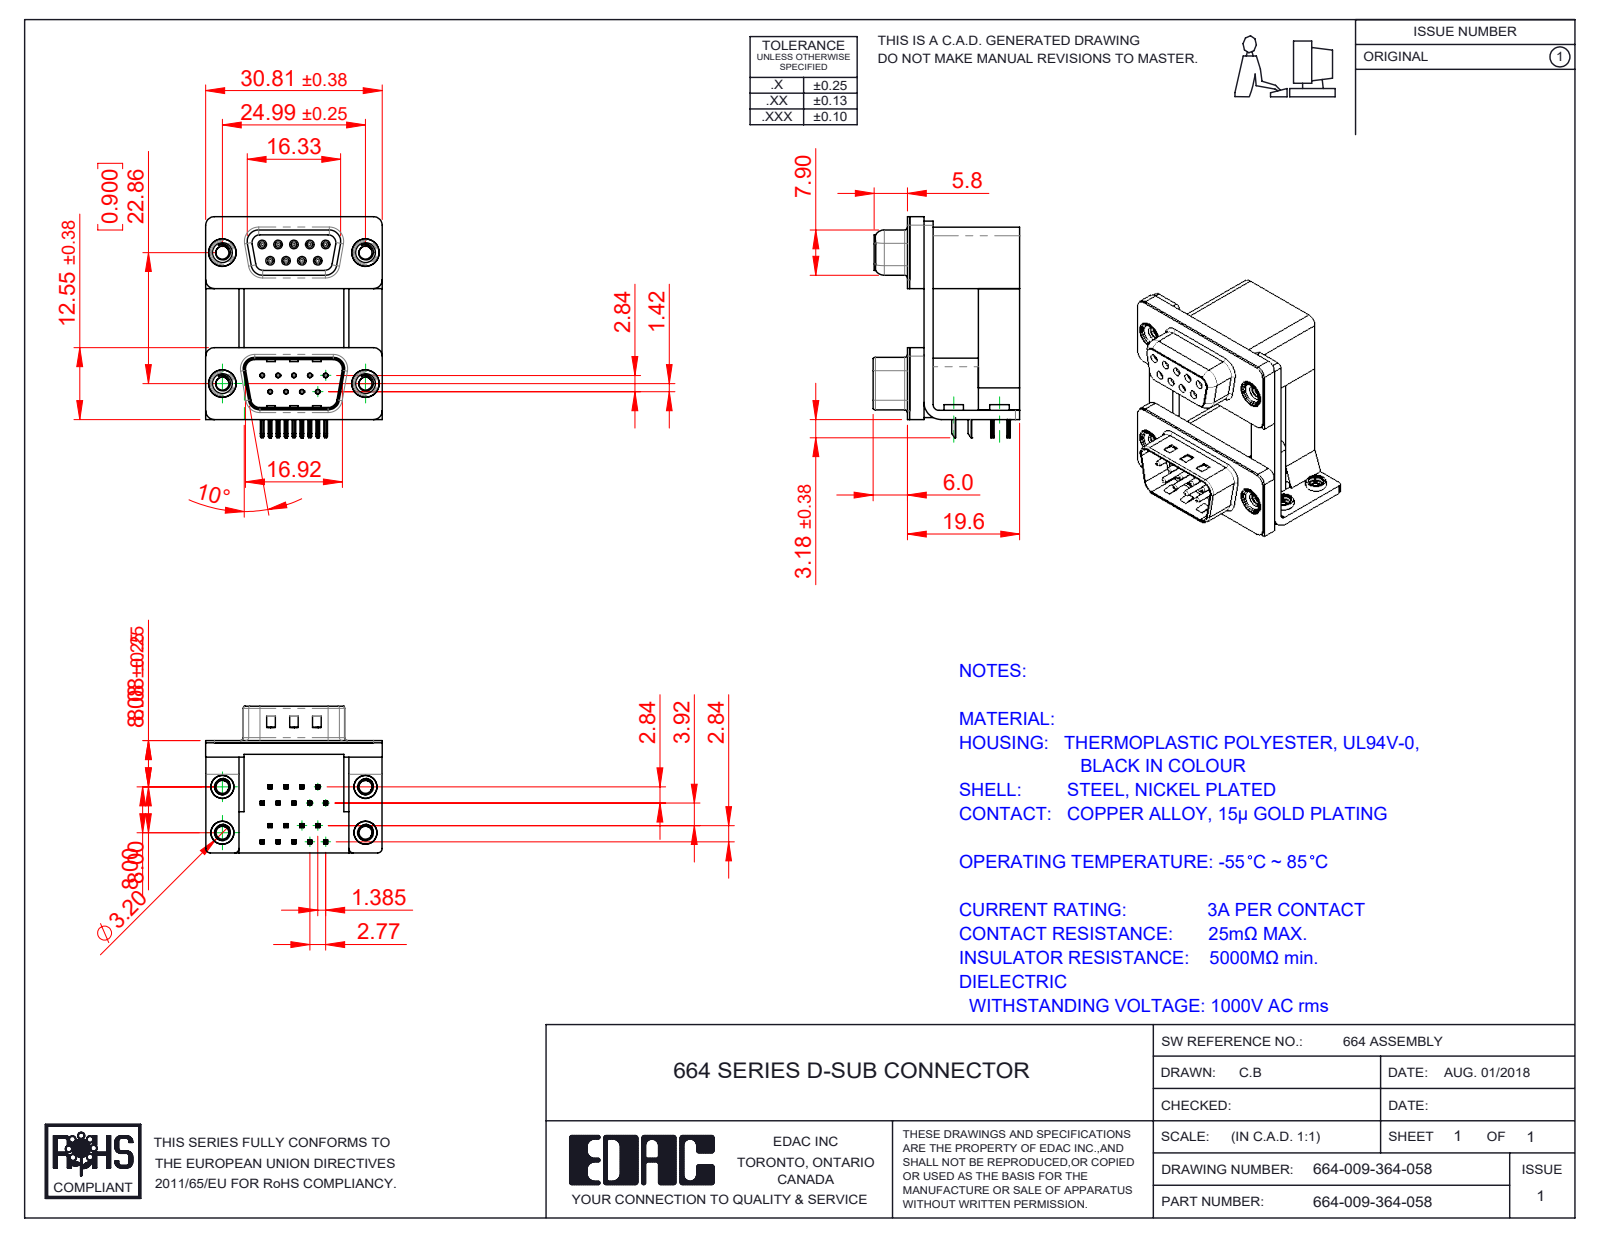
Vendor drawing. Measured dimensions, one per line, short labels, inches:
name: 664 Housing Upper_09 Contacts H; 664-009-364-058; 664 Contact Bottom Upper_H; 664 Threaded Rivet_4-40 (+8 more)
written by: SolidWorks 2020 (CONFIG_CONTROL_DESIGN)
unit: in
bodies: 33 solids, 2669 faces (1275 planar, 771 cylindrical, 623 other)
size: 1.519 × 1.213 × 1.008
volume: 0.693 in³; area: 20.63 in²
holes: 18× ⌀0.031, 9× ⌀0.014, 9× ⌀0.035, 8× ⌀0.089, 4× ⌀0.108, 4× ⌀0.126, 4× ⌀0.138, 4× ⌀0.157, 4× ⌀0.189, 4× ⌀0.197
bosses: 9× ⌀0.047, 9× ⌀0.03, 4× ⌀0.193, 4× ⌀0.187, 4× ⌀0.157, 4× ⌀0.154, 4× ⌀0.134
rounds: 72× R0.004, 36× R0.006, 36× R0.01, 18× R0.005, 18× R0.014, 13× R0.059, 12× R0.02, 9× R0.013
face distances: 0.016, 0.098, 0.657, 0.756, 0.472, 0.283, 0.374, 0.488, 0.063, 0.9
hole spacings: 0.124, 0.109, 0.907, 0.9, 0.218, 0.926, 0.79, 1.013
